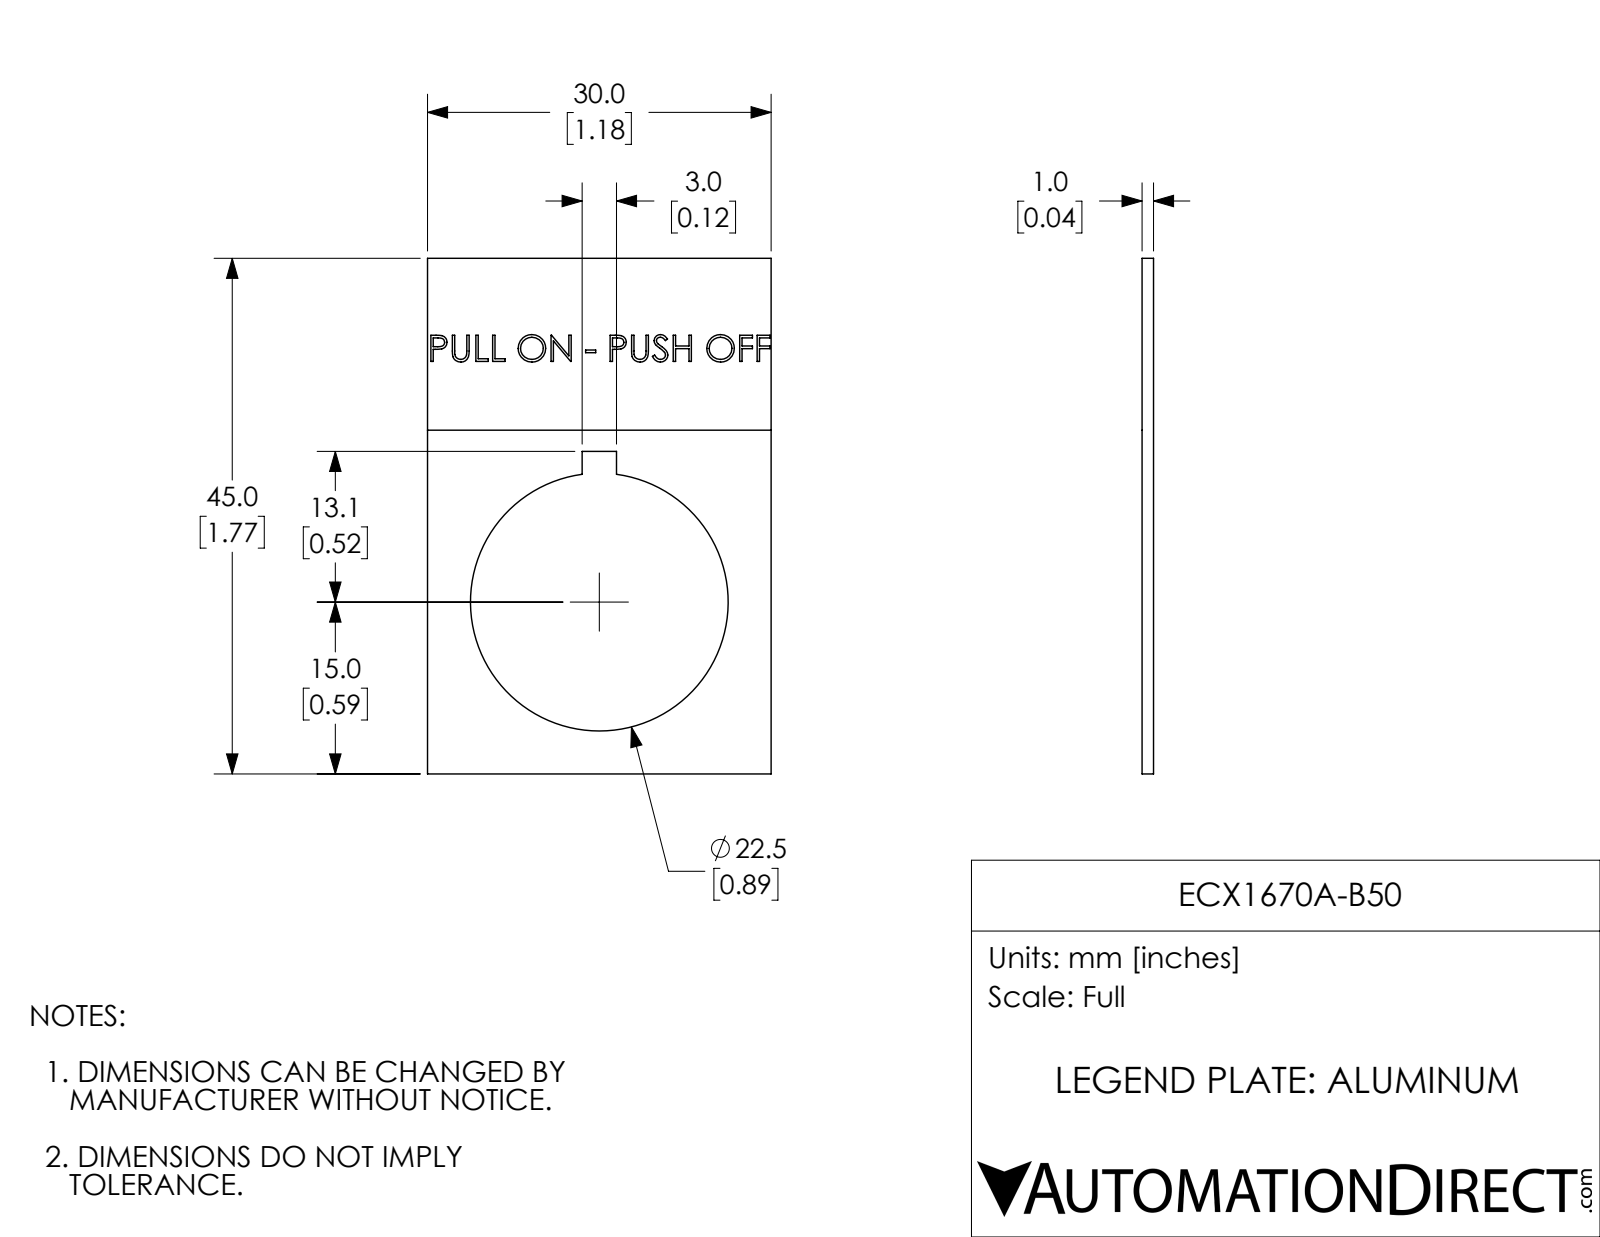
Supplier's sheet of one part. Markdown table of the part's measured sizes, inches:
| quantity | value |
| --- | --- |
| part name | ECX1670A-B50 |
| STEP written by | SolidWorks 2017 (AUTOMOTIVE_DESIGN) |
| units | inches |
| bodies | 1 solid, 176 faces (116 planar, 3 cylindrical, 57 other) |
| overall size | 1.772 × 1.181 × 0.039 |
| volume | 0.058 in³ |
| surface area | 3.288 in² |
| round holes (diameter × count) | 0.886 × 1 |
| main face-to-face distances | 0.039, 1.181, 1.772, 0.038, 0.531, 0.65, 1.108, 0.663, 0.118, 0.037 |
